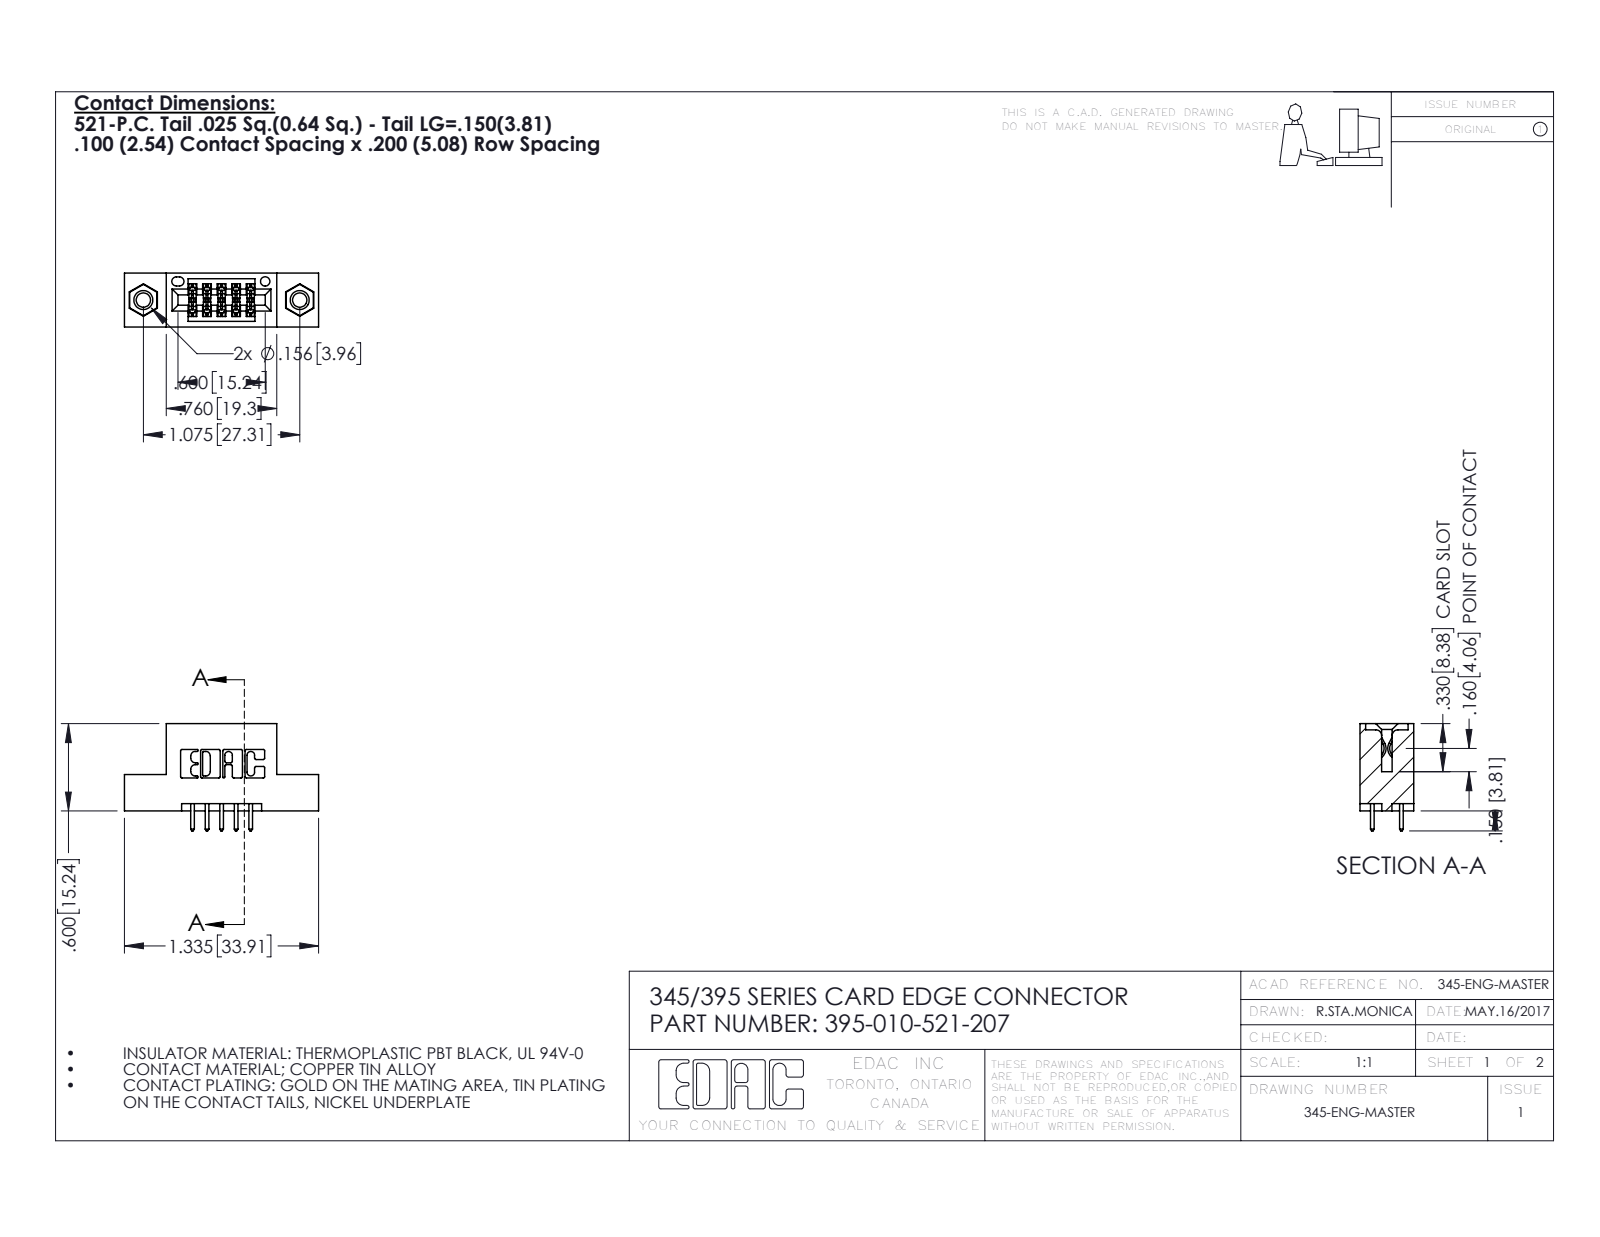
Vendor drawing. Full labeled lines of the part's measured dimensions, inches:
Part name (STEP PRODUCT): 345 Part_Flush Mounting Lugs - 0.156 Dia-TI; 395-010-521-207; 345-292-001_345-293-121; 345-250-001_345-250-005-103
STEP written by: SolidWorks 2016 (CONFIG_CONTROL_DESIGN)
Units: inches
Bodies: 13 solids, 686 faces (442 planar, 228 cylindrical, 16 other)
Overall size (bounding box): 1.335 × 0.737 × 0.37
Volume: 0.179 in³ · Surface area: 5.611 in²
Round holes (diameter × count): ⌀0.098 ×2, ⌀0.125 ×2, ⌀0.156 ×2, ⌀0.064 ×1
Round bosses / shafts (diameter × count): ⌀0.155 ×2
Partial cylindrical surfaces — rounded edges, fillets, slot ends (radius × count): R0.01 ×22, R0.006 ×15, R0.01 ×10, R0.007 ×6, R0.031 ×6, R0.026 ×3, R0.014 ×2, R0.019 ×2
Main face-to-face distances: 0.2, 0.37, 0.072, 0.298, 0.1, 0.098, 0.272, 0.025, 0.35, 0.25
Hole centre spacings: 0.27, 0.847, 1.075
